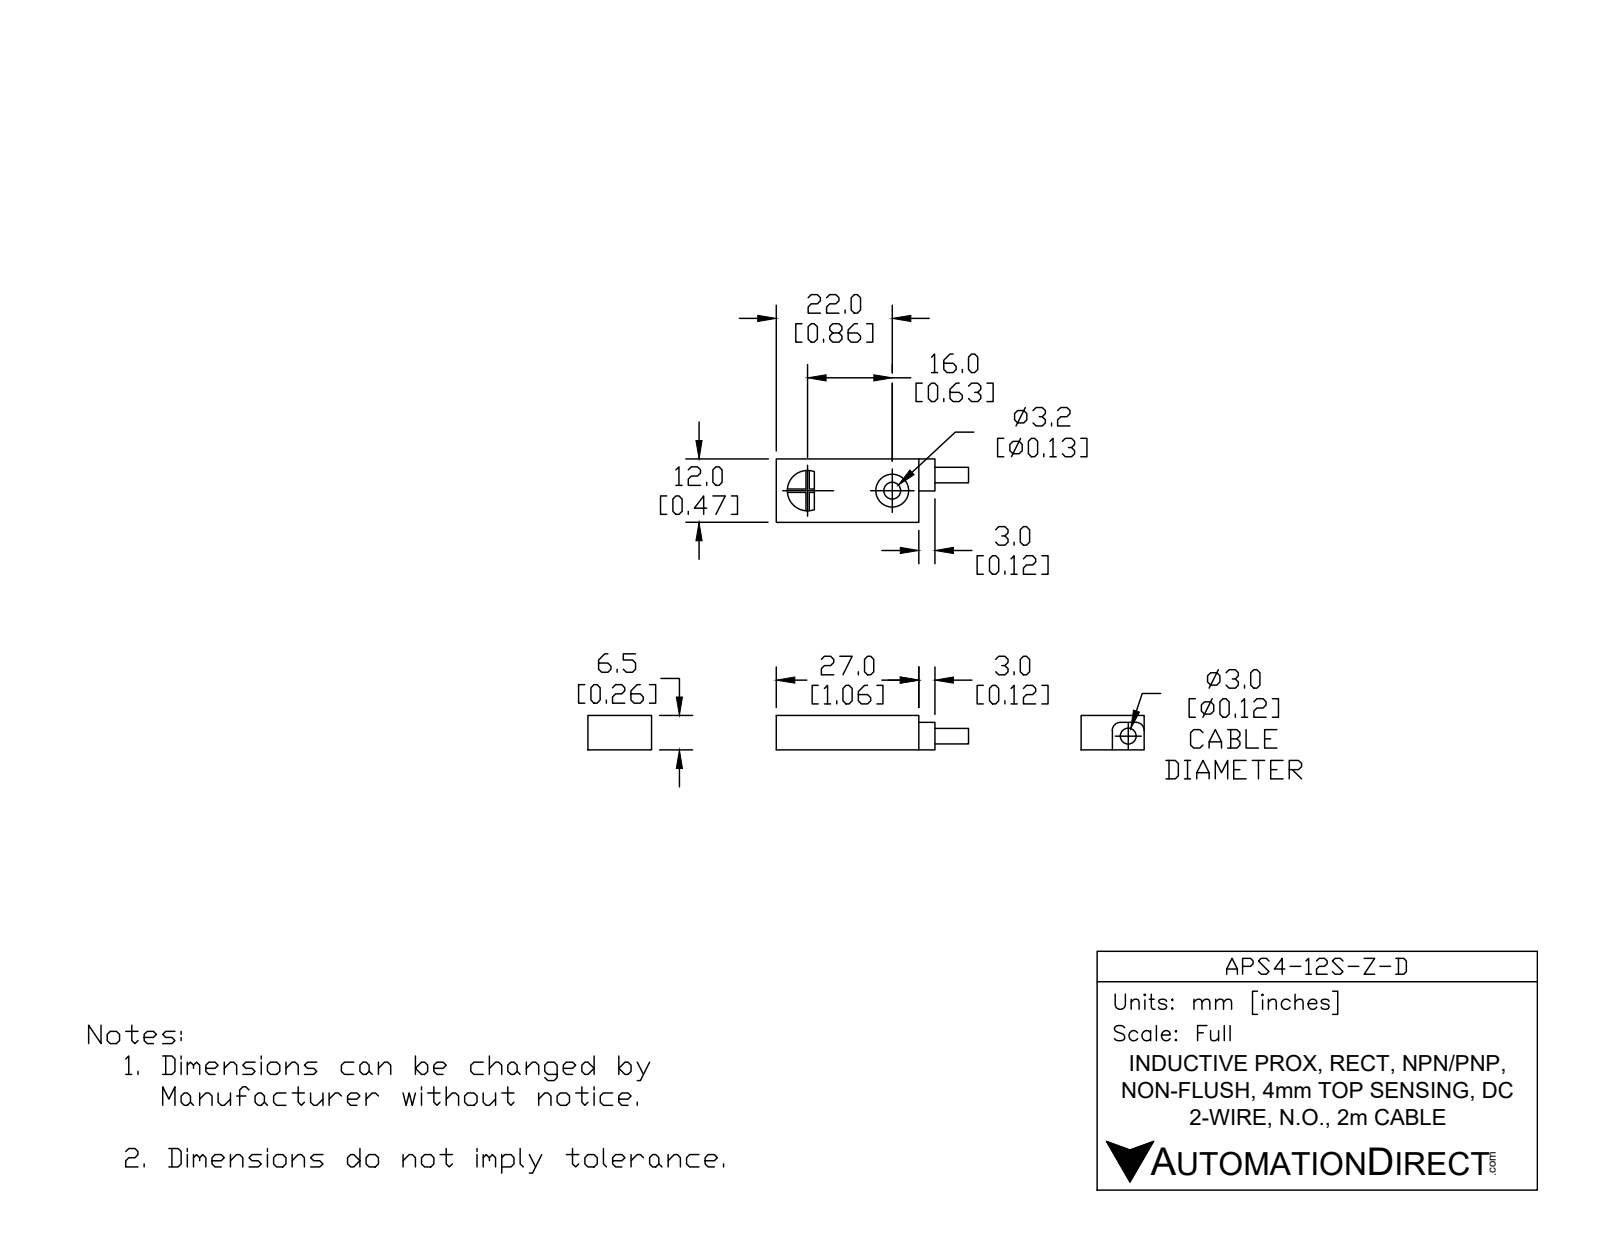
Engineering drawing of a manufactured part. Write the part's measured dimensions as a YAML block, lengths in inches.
part_name: "APS4-12S-Z-D"
step_written_by: "SolidWorks 2017 (AUTOMOTIVE_DESIGN)"
units: inches
bodies: {solids: 4, faces: 88, planar: 60, cylindrical: 28, other: 0}
overall_size: [1.611, 0.516, 0.285]
volume: 0.081
surface_area: 5.203
round_holes:
  - {diameter: 0.081, count: 1}
  - {diameter: 0.126, count: 1}
  - {diameter: 0.217, count: 1}
  - {diameter: 0.232, count: 1}
  - {diameter: 0.245, count: 1}
round_bosses_or_shafts:
  - {diameter: 0.345, count: 1}
  - {diameter: 0.226, count: 1}
  - {diameter: 0.112, count: 1}
partial_cylinders:
  - {radius: 0.005, count: 8}
  - {radius: 0.02, count: 4}
  - {radius: 0.031, count: 2}
face_to_face_distances: [0.05, 0.26, 0.012, 0.422, 0.272, 0.272, 0.284, 0.022, 0.25, 0.262]
hole_center_spacings: [0.629]
